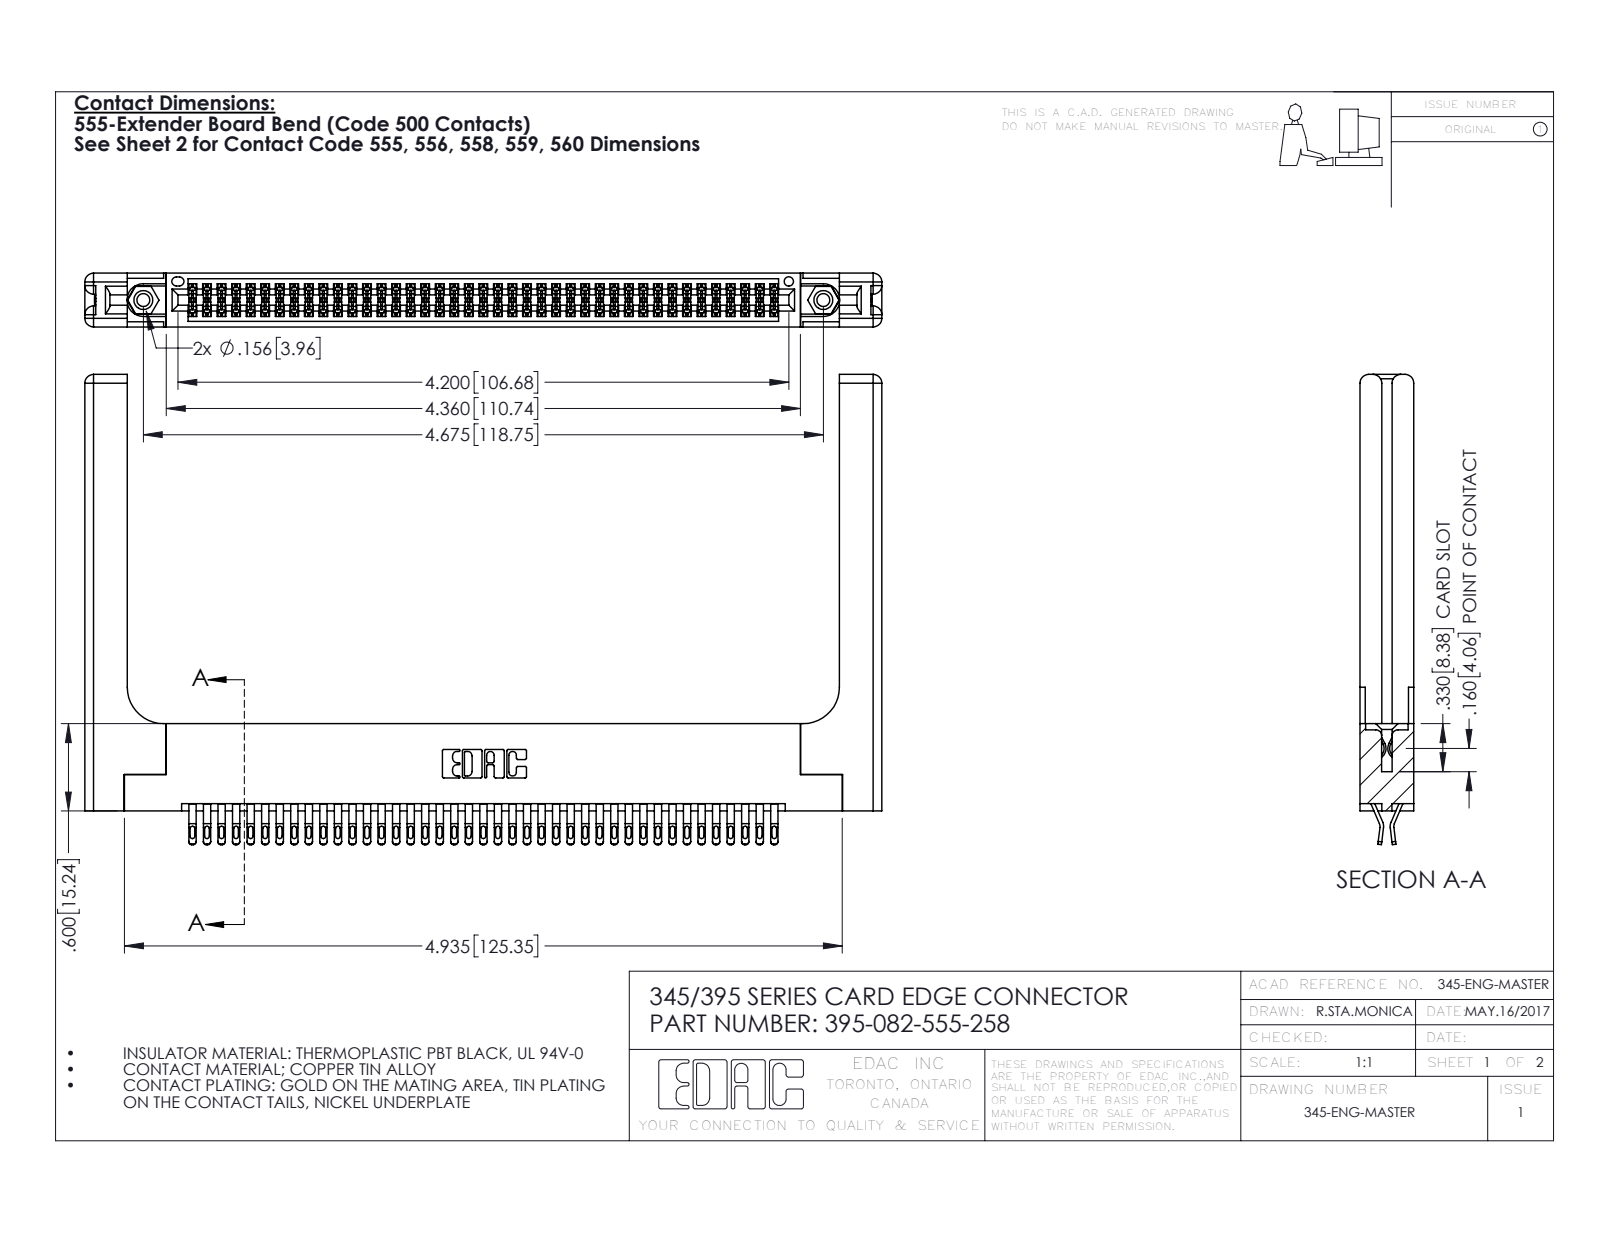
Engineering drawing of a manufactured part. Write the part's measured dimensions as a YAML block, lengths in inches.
part_name: "345-220-058_345-220-058; 345-292-001_555 Tail; 345 Part_Flush Mounting Lugs - 0.156 Dia-TH; 345-250-001_345-250-001-102 (+1 more)"
step_written_by: "SolidWorks 2016 (CONFIG_CONTROL_DESIGN)"
units: inches
bodies: {solids: 87, faces: 4974, planar: 2770, cylindrical: 2144, other: 60}
overall_size: [5.479, 3.232, 0.37]
volume: 1.356
surface_area: 40.59
round_holes:
  - {diameter: 0.089, count: 2}
  - {diameter: 0.125, count: 2}
  - {diameter: 0.156, count: 2}
  - {diameter: 0.064, count: 1}
round_bosses_or_shafts:
  - {diameter: 0.155, count: 2}
partial_cylinders:
  - {radius: 0.016, count: 205}
  - {radius: 0.02, count: 164}
  - {radius: 0.006, count: 123}
  - {radius: 0.01, count: 22}
  - {radius: 0.06, count: 16}
  - {radius: 0.007, count: 6}
  - {radius: 0.031, count: 6}
  - {radius: 0.026, count: 3}
face_to_face_distances: [0.072, 0.37, 0.298, 0.025, 0.2, 0.098, 0.272, 0.225, 0.148, 0.15]
hole_center_spacings: [0.27, 4.439, 4.675]
